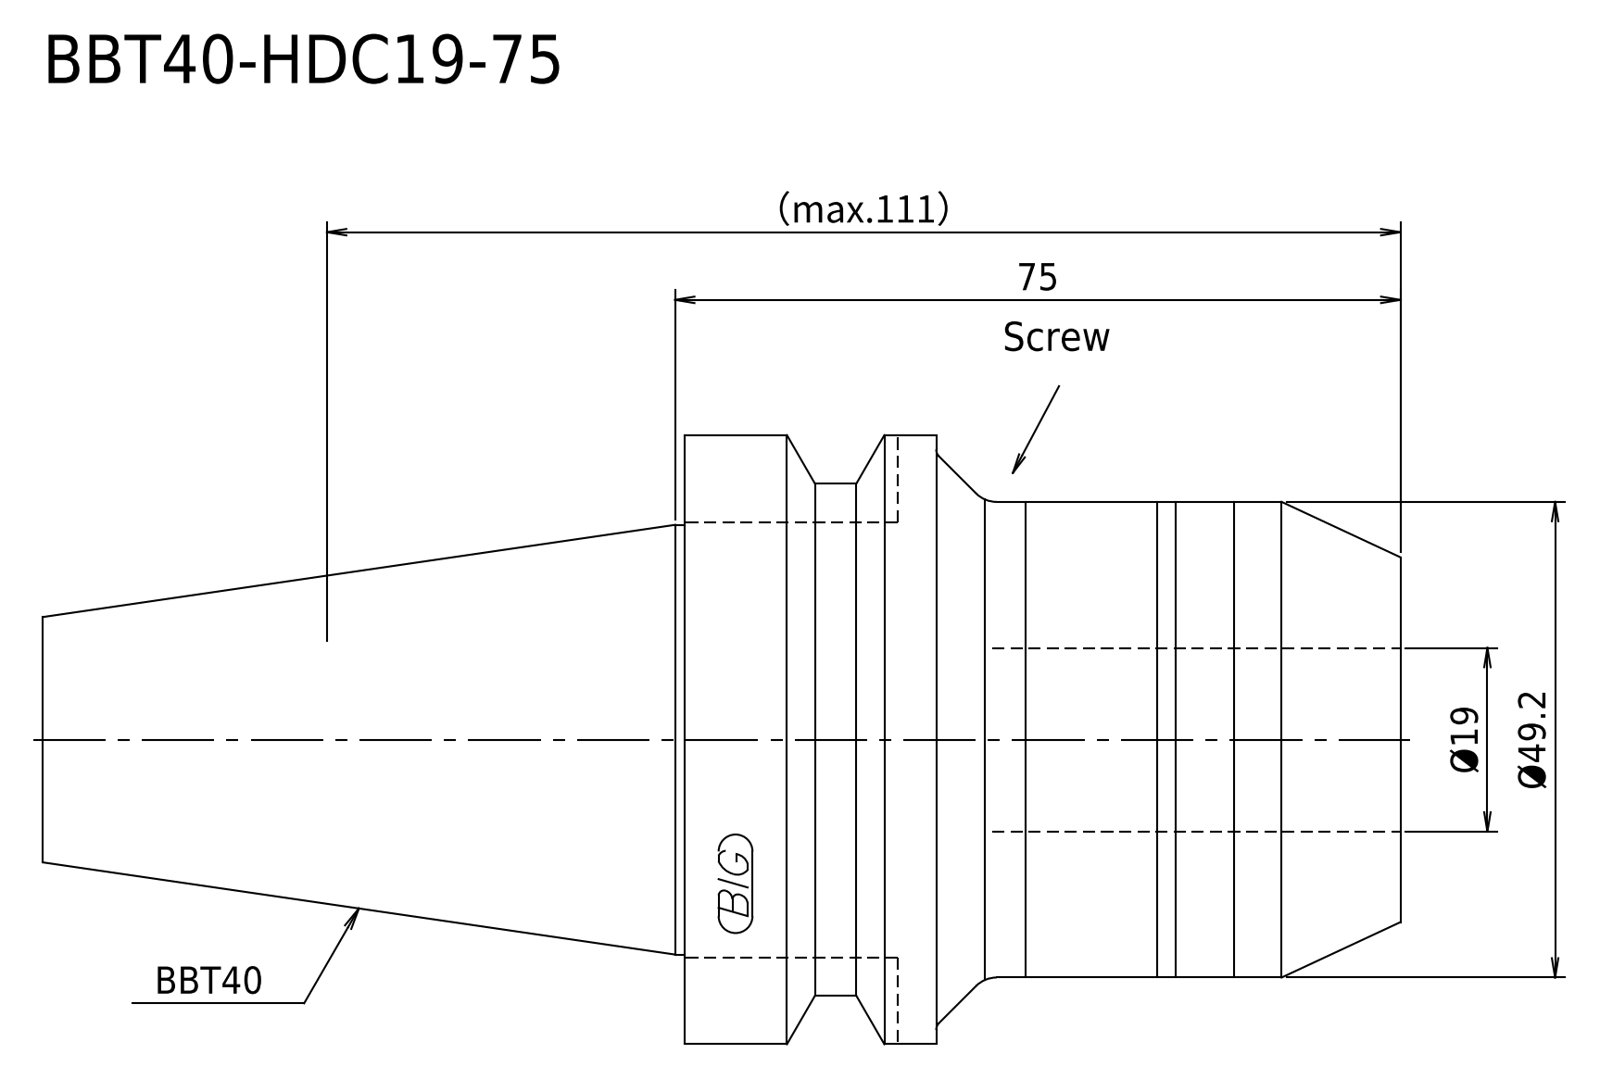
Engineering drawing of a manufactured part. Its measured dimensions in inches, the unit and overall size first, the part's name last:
Units: inches
Overall size (bounding box): 5.528 × 2.48 × 2.48
Round bosses / shafts (diameter × count): ⌀2.48 ×1, ⌀2.087 ×1, ⌀1.937 ×1, ⌀1.75 ×1
Main face-to-face distances: 2.886, 5.5, 2.614, 0.028, 2.913, 5.528, 1.89, 1.862, 1.024, 3.638
Volume: 13.92 in³ · Surface area: 38.21 in²
Bodies: 1 solid, 18 faces (5 planar, 5 cylindrical, 8 other)
STEP written by: Kubotek KeyCreator V8.5.1 (14335) (CONFIG_CONTROL_DESIGN)
